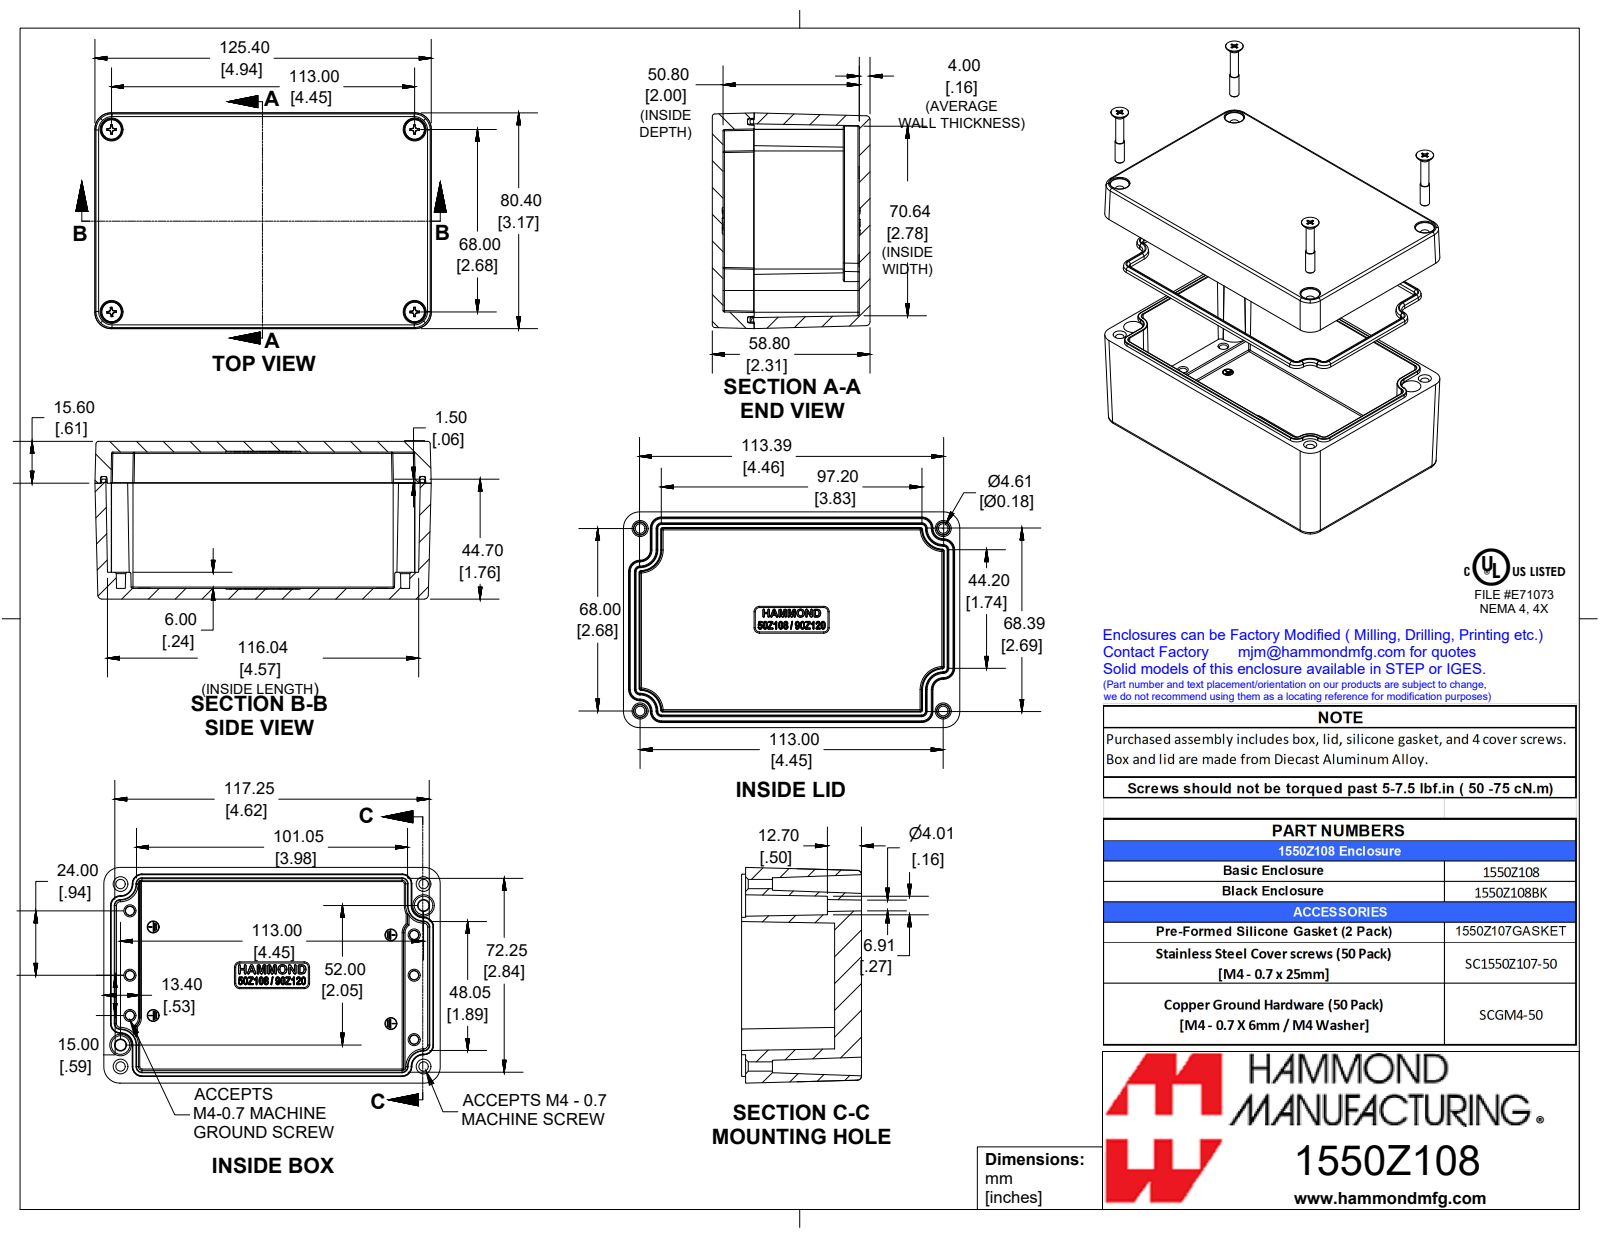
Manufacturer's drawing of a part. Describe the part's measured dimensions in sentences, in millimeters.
The part is named "1550Z108". Its 3-D file was written by "SolidWorks 2019 (AUTOMOTIVE_DESIGN)". It is 7 solids with 1491 faces: 399 planar, 220 cylindrical and 872 other. Overall it measures 125.4 by 80.4 by 58.8 millimeters. Its volume is 179 900 cubic millimeters and its surface area 93 550 square millimeters. Round holes: 4 of diameter 3.6. Round bosses or shafts: 4 of diameter 7.6, 4 of diameter 3.9, 4 of diameter 3.3. Partial cylindrical surfaces (rounded edges, fillets, slot ends): 46 of radius 0.2, 28 of radius 0.5, 24 of radius 1, 20 of radius 0.3, 8 of radius 6, 4 of radius 1.5, 2 of radius 4. The main face-to-face distances are 4, 54.8, 58.8, 50.8, 80.4, 11.6, 15.6, 43.2, 39.2, 70.3. The hole center spacings are 68, 113, 131.9.
